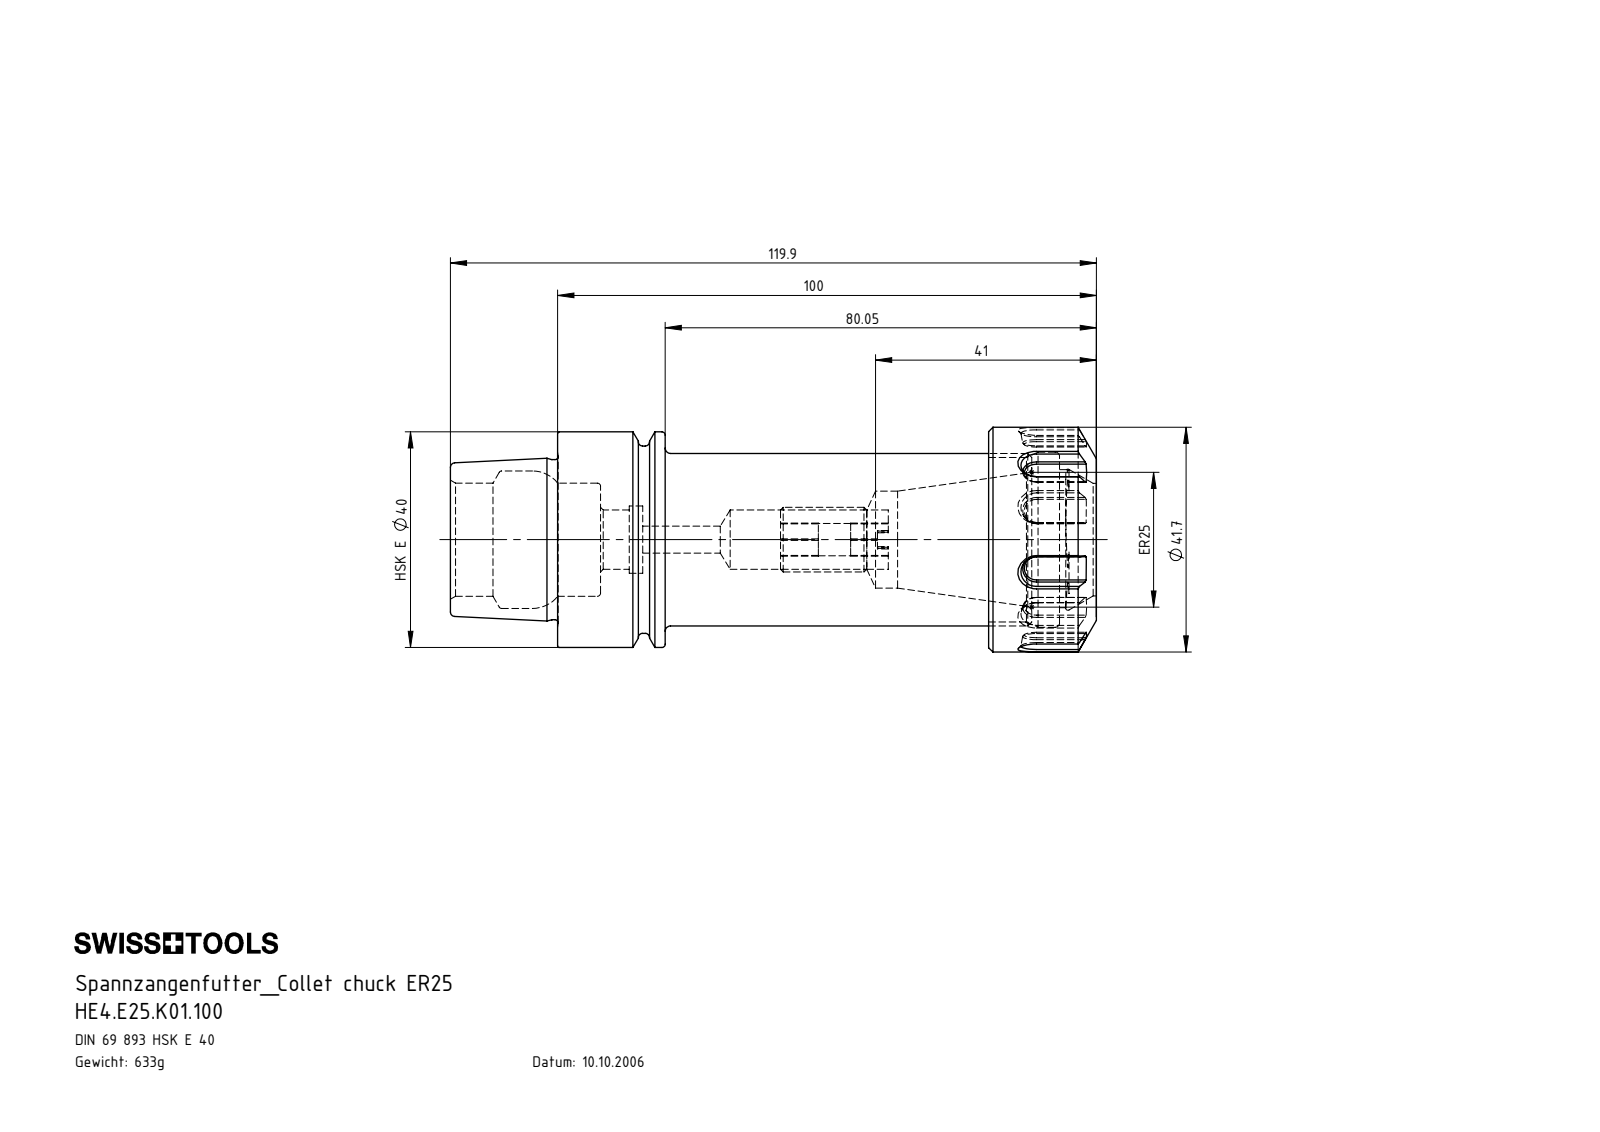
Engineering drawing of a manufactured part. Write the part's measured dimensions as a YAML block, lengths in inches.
part_name: "HE4-E25.K01.100_A_Fertigbearbeitung; E25-ER1.001.020; ERU-AN5.K01.020_A; HE4.E25.K01.100"
step_written_by: "SolidWorks 2017 (CONFIG_CONTROL_DESIGN)"
units: inches
bodies: {solids: 3, faces: 224, planar: 92, cylindrical: 43, other: 89}
overall_size: [4.72, 1.642, 1.642]
volume: 4.922
surface_area: 41.13
round_holes:
  - {diameter: 0.197, count: 1}
  - {diameter: 0.236, count: 1}
  - {diameter: 0.433, count: 1}
  - {diameter: 0.492, count: 1}
  - {diameter: 0.709, count: 1}
  - {diameter: 0.823, count: 1}
  - {diameter: 0.827, count: 1}
  - {diameter: 1.004, count: 1}
  - {diameter: 1.201, count: 1}
  - {diameter: 1.28, count: 1}
round_bosses_or_shafts:
  - {diameter: 1.642, count: 1}
  - {diameter: 1.575, count: 1}
  - {diameter: 1.368, count: 1}
  - {diameter: 1.26, count: 1}
  - {diameter: 1.17, count: 1}
  - {diameter: 0.472, count: 1}
partial_cylinders:
  - {radius: 0.479, count: 2}
face_to_face_distances: [3.152, 0.787, 3.15, 0.472, 3.937, 0.785, 2.364, 3.667, 2.882, 0.518]
